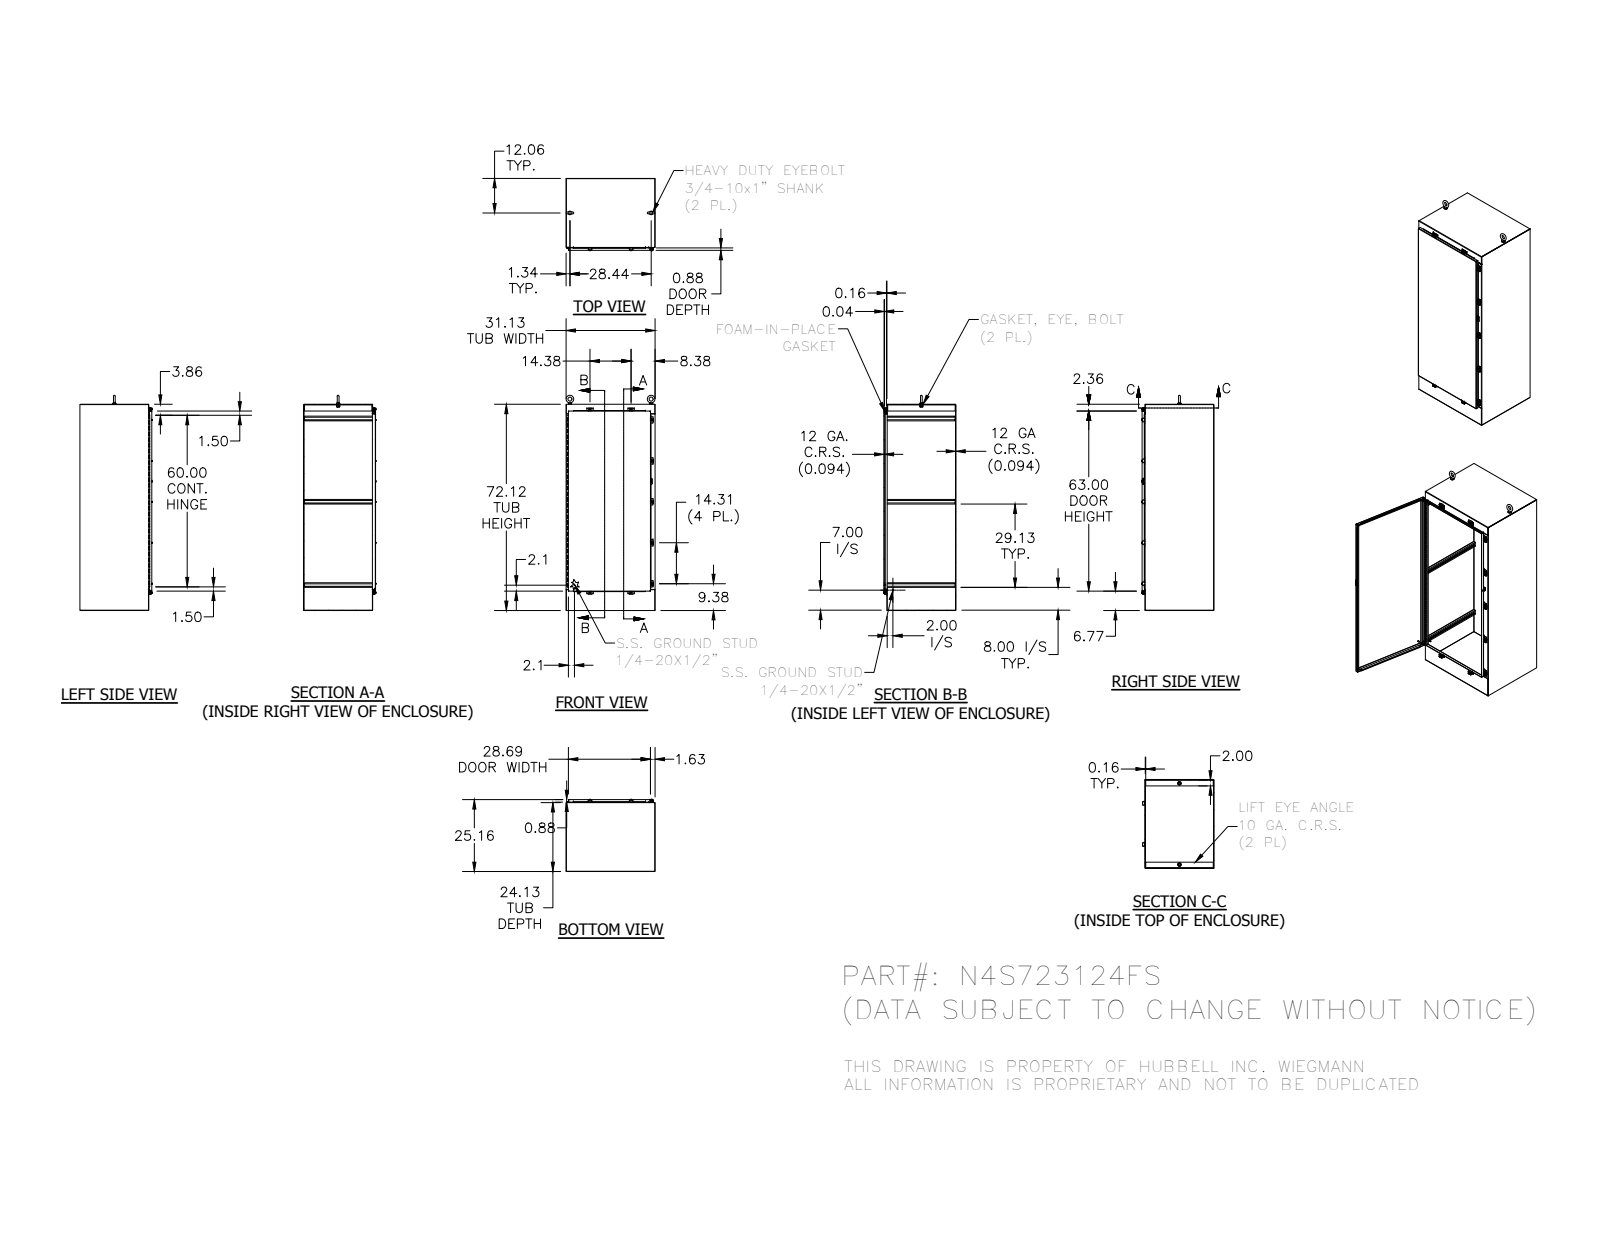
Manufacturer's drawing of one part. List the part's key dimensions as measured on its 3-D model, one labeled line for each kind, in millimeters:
Part name (STEP PRODUCT): HSSN1300W60_1; N4S723124FSBTM_1; HSSN1300W60L_1; 316298_1 (+8 more)
STEP written by: SolidWorks 2014 (AUTOMOTIVE_DESIGN)
Units: millimetres
Bodies: 78 solids, 3000 faces (1210 planar, 1210 cylindrical, 580 other)
Overall size (bounding box): 1911.3 × 790.6 × 644
Volume: 18 270 000 mm³ · Surface area: 14 830 000 mm²
Round holes (diameter × count): ⌀5.4 ×9, ⌀7.1 ×9, ⌀7.6 ×9, ⌀2.8 ×3, ⌀16.3 ×2, ⌀20.7 ×2, ⌀3.2 ×1, ⌀4 ×1, ⌀12.7 ×1
Round bosses / shafts (diameter × count): ⌀6.4 ×12, ⌀13.2 ×9, ⌀12.7 ×9, ⌀8.9 ×9, ⌀31.8 ×2, ⌀28.4 ×2, ⌀19.1 ×2, ⌀8.6 ×2
Partial cylindrical surfaces — rounded edges, fillets, slot ends (radius × count): R0.8 ×107, R3.2 ×43, R1.6 ×22, R6.4 ×21, R0.8 ×19, R0.5 ×18, R1.3 ×18, R2.2 ×18
Main face-to-face distances: 2.4, 636.7, 788.2, 634.3, 639.1, 785.8, 790.6, 1829.6, 610.4, 26.3
Hole centre spacings: 363.6, 727.1, 20, 365.3, 1090.7, 1635.1, 1675.4, 11.4
